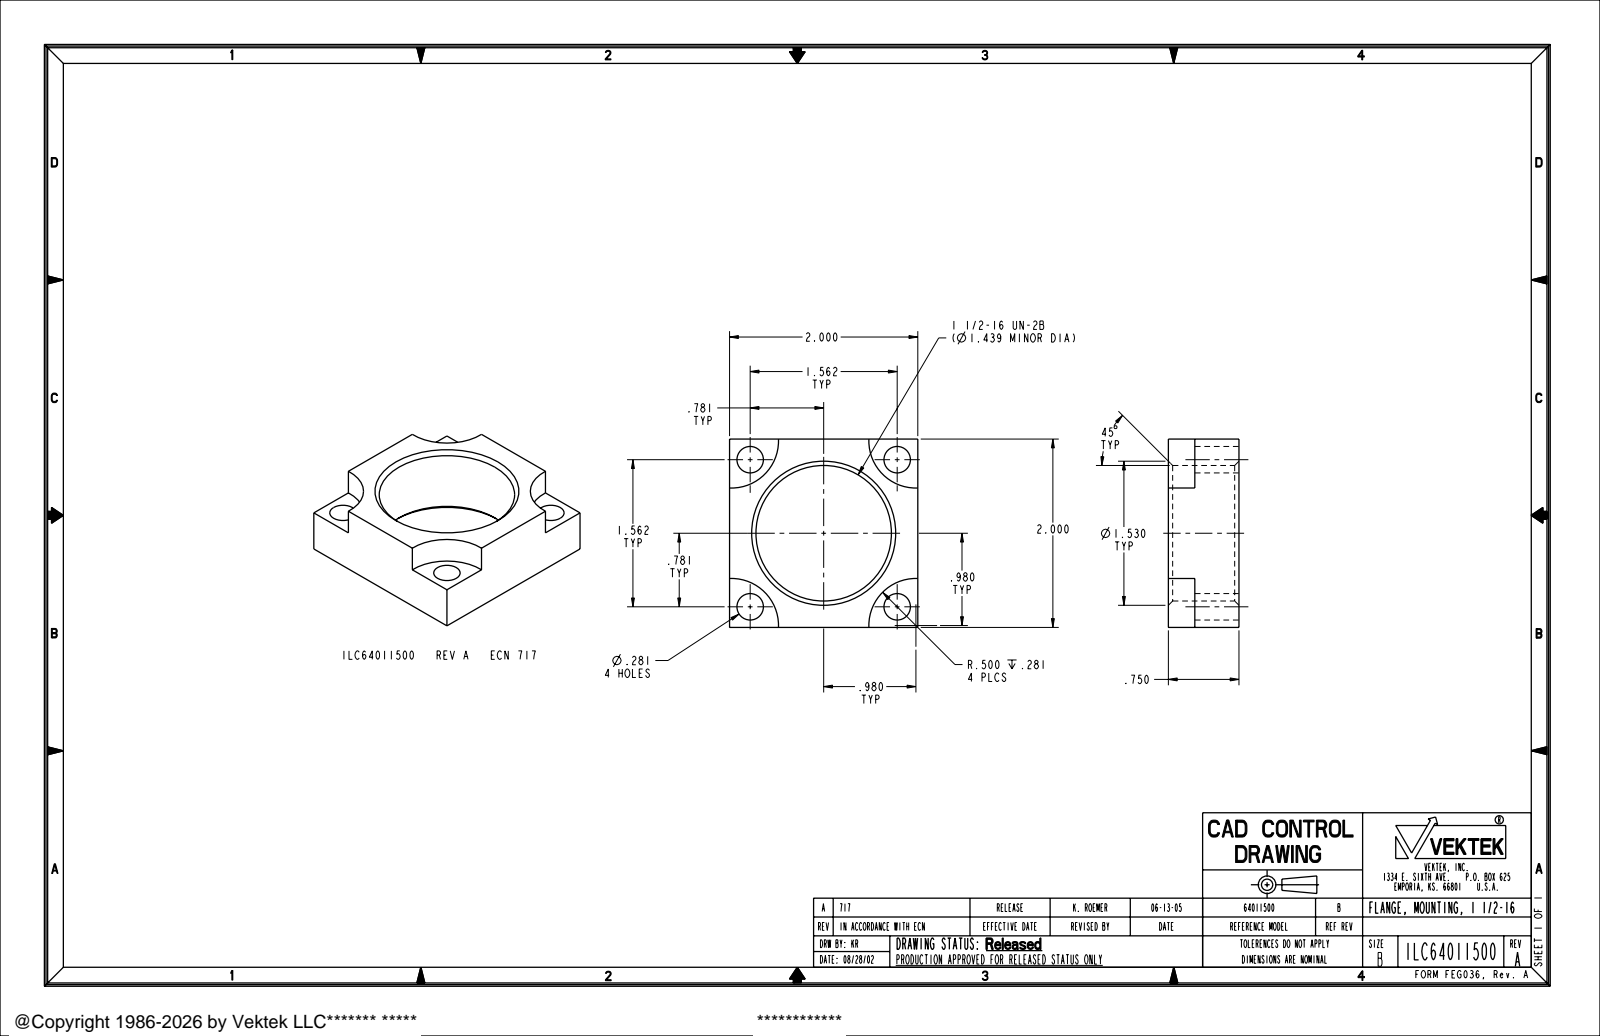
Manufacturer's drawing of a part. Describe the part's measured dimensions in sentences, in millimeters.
The part is named "ILC64011500". Its 3-D file was written by "PRO/ENGINEER BY PARAMETRIC TECHNOLOGY CORPORATION, 2004290 (AUTOMOTIVE_DESIGN_CC2)". It is 1 solid with 28 faces: 10 planar, 14 cylindrical and 4 other. Overall it measures 50.8 by 50.8 by 19.1 millimeters. Its volume is 23 120 cubic millimeters and its surface area 9 561 square millimeters. Round holes: 4 of diameter 7.1, 1 of diameter 36.6. Partial cylindrical surfaces (rounded edges, fillets, slot ends): 4 of radius 12.7. The main face-to-face distances are 50.8, 19.1, 11.9, 7.1. The hole center spacings are 28.1, 39.7, 56.1.
